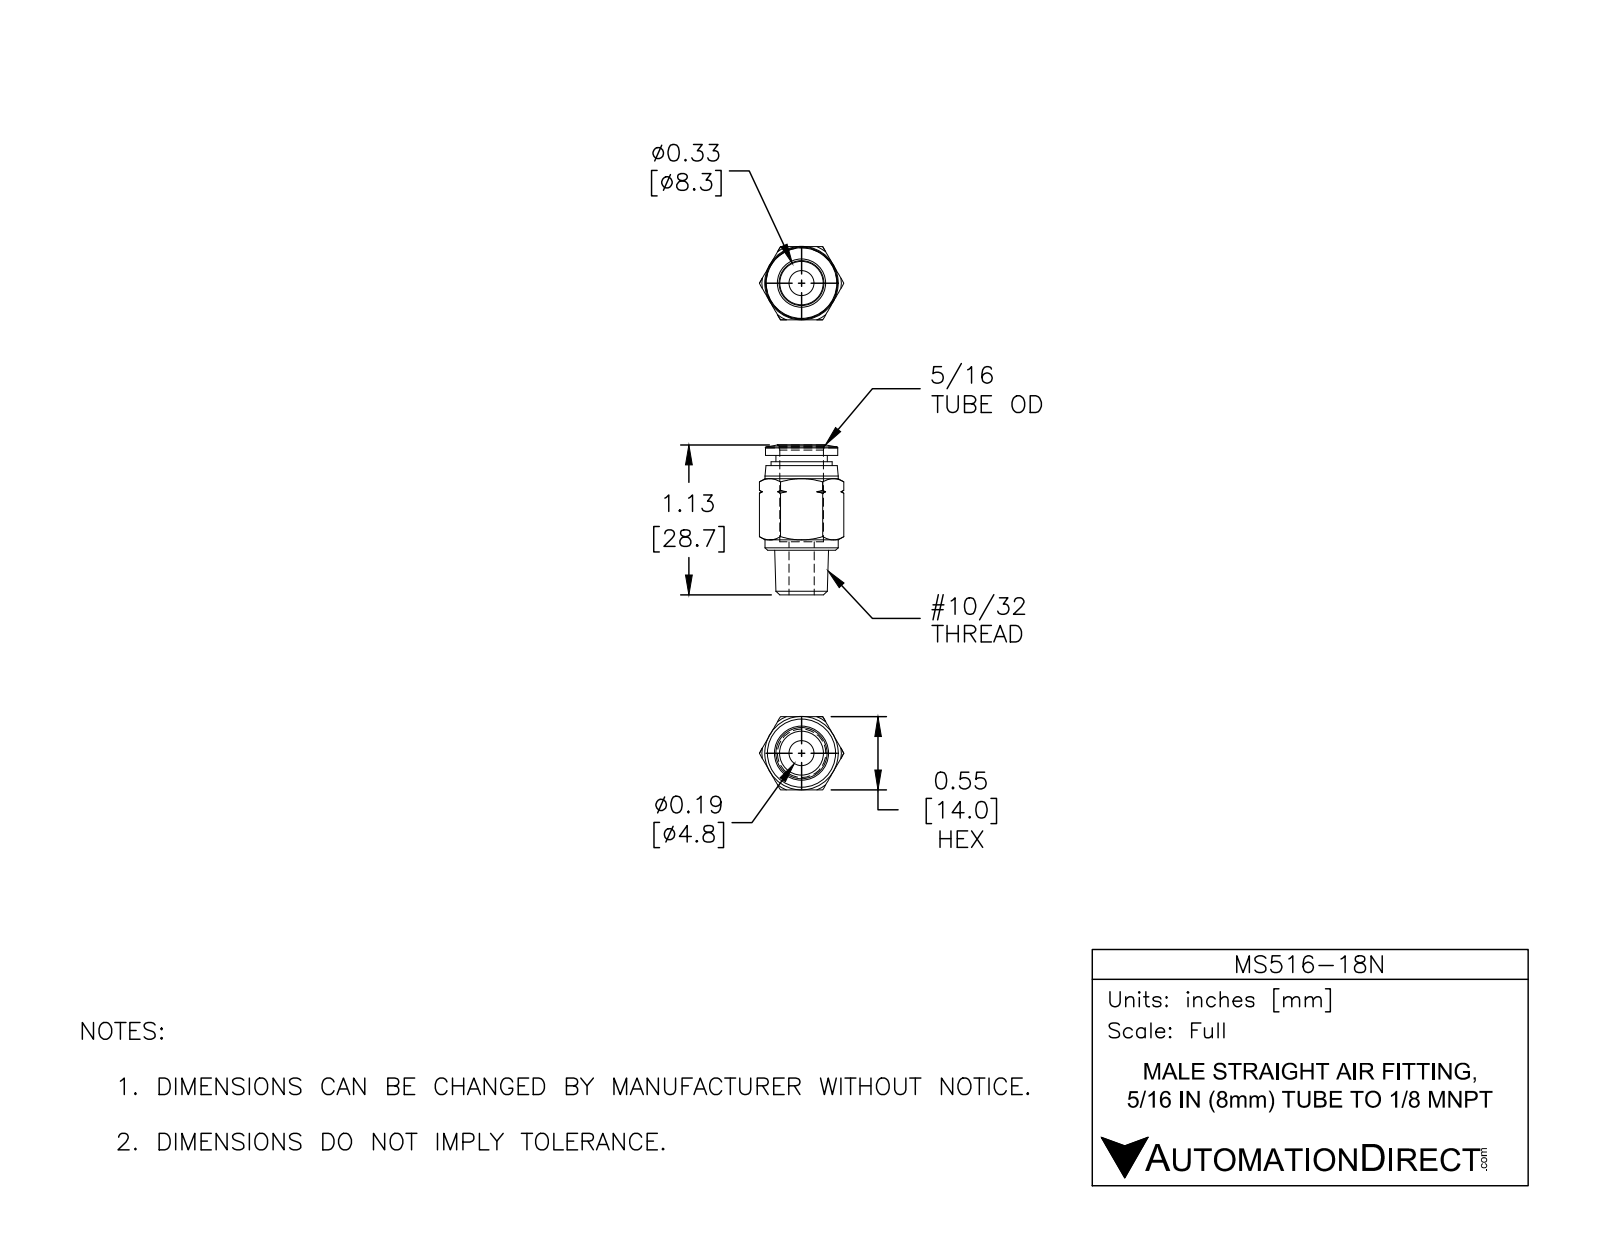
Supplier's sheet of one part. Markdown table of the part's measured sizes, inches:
| quantity | value |
| --- | --- |
| part name | MS516-18N |
| STEP written by | SolidWorks 2015 (CONFIG_CONTROL_DESIGN) |
| units | inches |
| bodies | 1 solid, 66 faces (12 planar, 14 cylindrical, 40 other) |
| overall size | 1.128 × 0.636 × 0.551 |
| volume | 0.158 in³ |
| surface area | 3.394 in² |
| round holes (diameter × count) | 0.189 × 1, 0.327 × 1 |
| round bosses / shafts (diameter × count) | 0.551 × 1, 0.543 × 1, 0.461 × 1, 0.386 × 1 |
| main face-to-face distances | 0.551, 0.715, 0.638, 0.077, 0.335, 0.972, 1.049, 0.4, 0.065, 0.573 |
